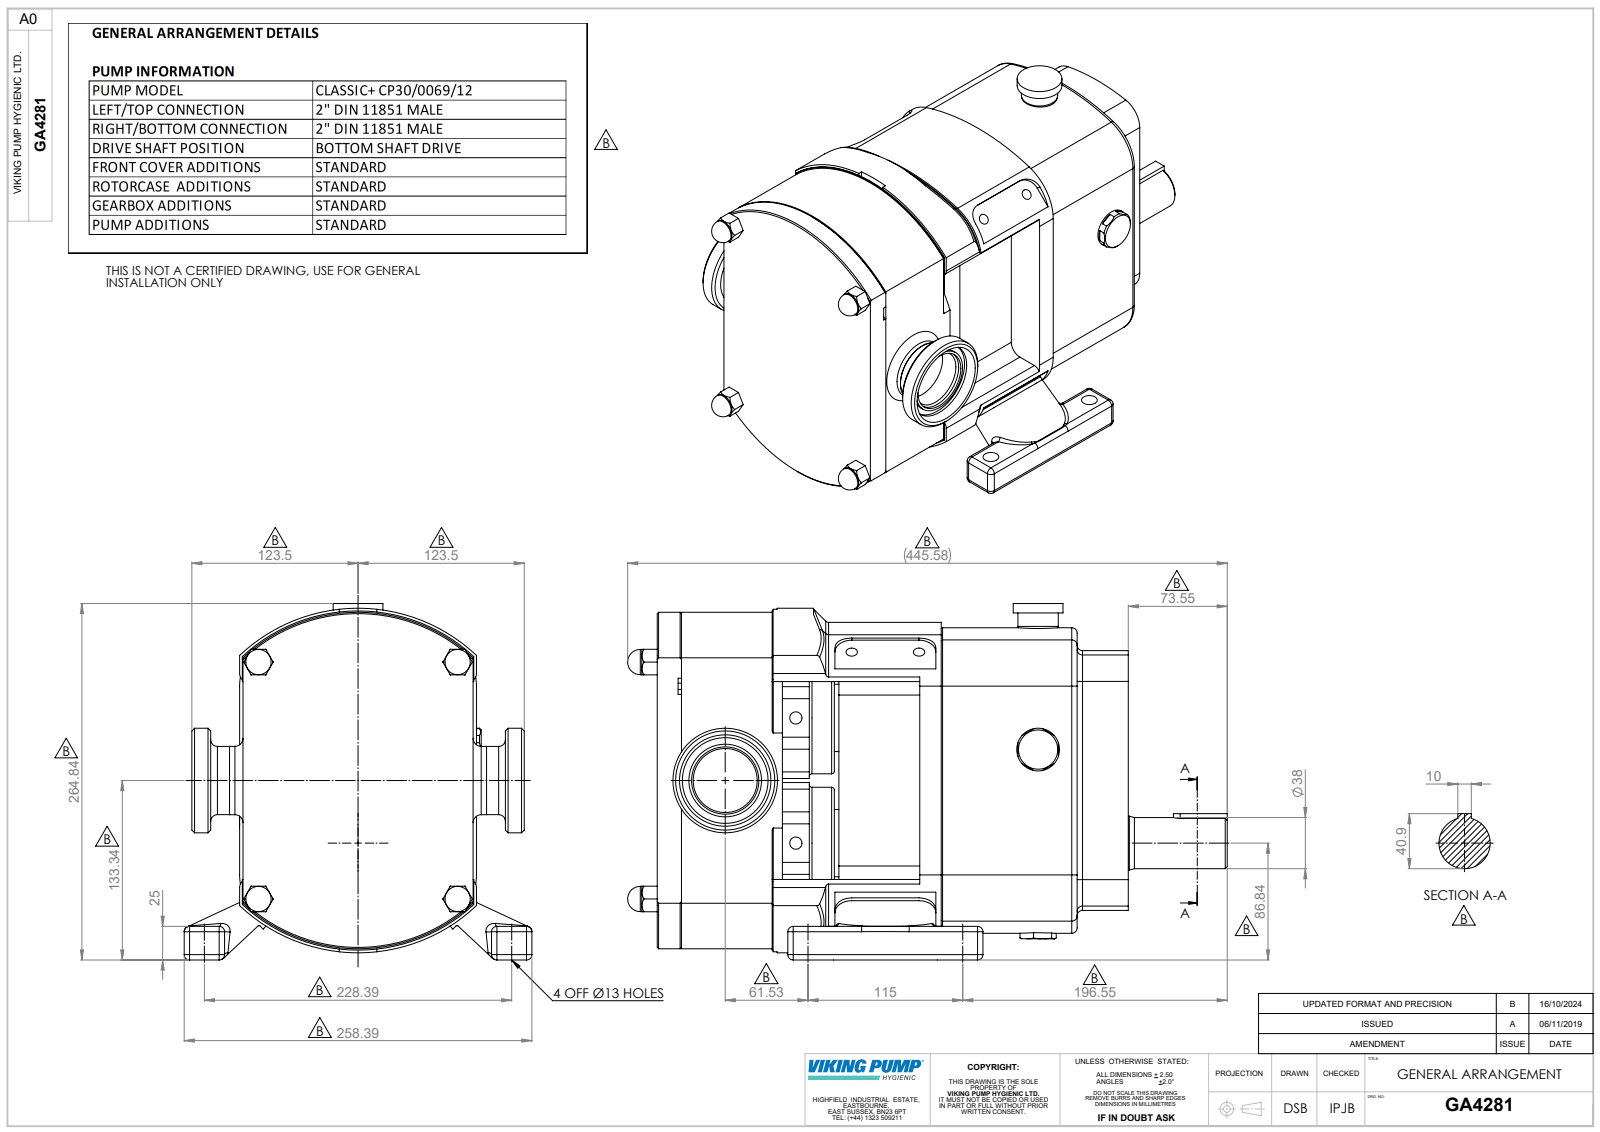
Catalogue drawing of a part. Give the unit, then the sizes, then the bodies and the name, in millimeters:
Units: millimetres
Overall size (bounding box): 445.58 × 264.84 × 258.38
Round holes (diameter × count): ⌀8.5 ×4, ⌀10.11 ×4, ⌀13 ×4, ⌀9.09 ×2, ⌀35 ×1, ⌀47.6 ×1, ⌀50 ×1, ⌀63.7 ×1
Round bosses / shafts (diameter × count): ⌀18.8 ×4, ⌀83 ×2, ⌀50 ×2, ⌀77.7 ×1, ⌀54 ×1, ⌀50.8 ×1, ⌀50.7 ×1, ⌀40.01 ×1
Partial cylindrical surfaces — rounded edges, fillets, slot ends (radius × count): R4 ×44, R1 ×16, R10 ×12, R6 ×10, R12.5 ×4, R12.57 ×4, R12.6 ×4, R20 ×4
Main face-to-face distances: 1.5, 169.5, 139, 38, 134.98, 29, 215.05, 350.03, 30.5, 140.5
Hole centre spacings: 63.64, 50.05, 70.13, 90, 115, 127.18, 205.62, 228.38
Volume: 11 500 000 mm³ · Surface area: 532 868 mm²
Bodies: 3 solids, 740 faces (271 planar, 250 cylindrical, 219 other)
Part name (STEP PRODUCT): GA4281; Copy of CP30-0069-12 H B^GA4281; Copy of Z94-5031-33 - 2 INCH DIN11851^GA4281
STEP written by: SolidWorks 2023 (AUTOMOTIVE_DESIGN)
